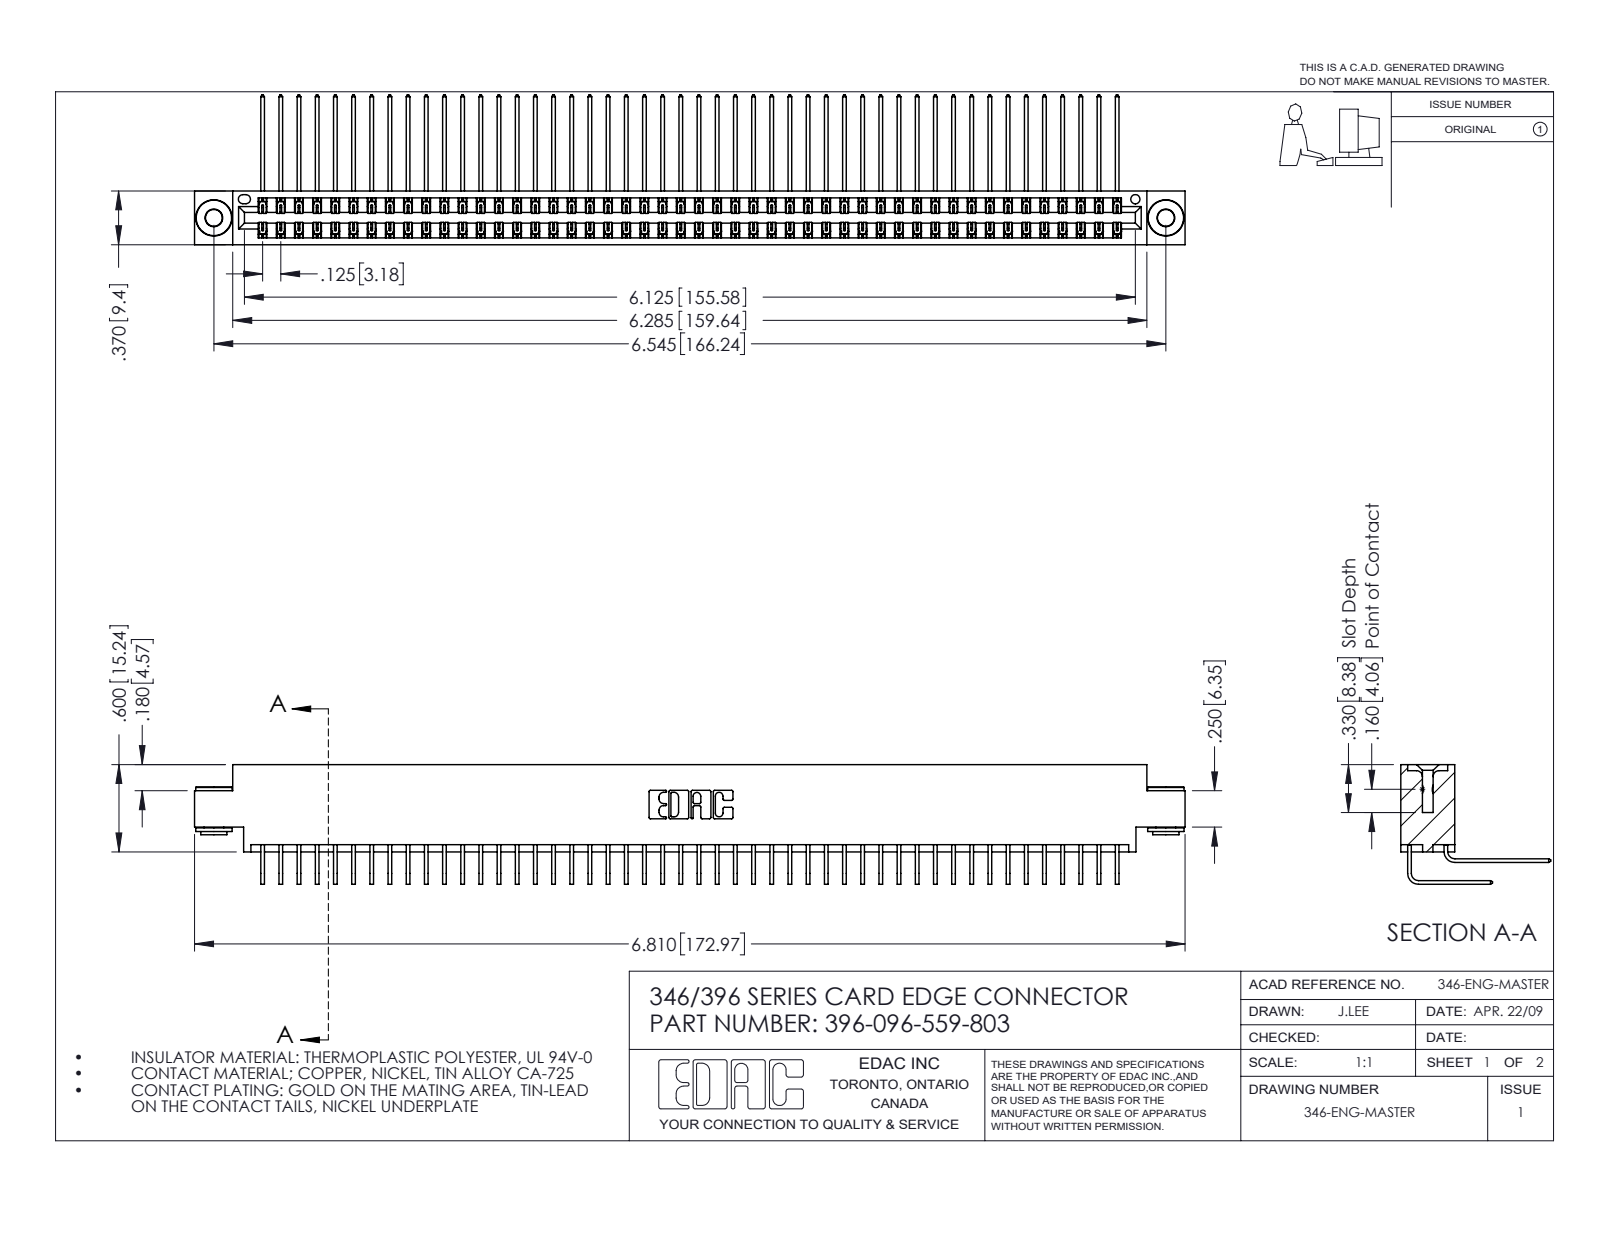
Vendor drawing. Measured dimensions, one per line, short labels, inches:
name: 396-096-559-803; 345-250-002_345-250-002-102; 346 Part_0.170 Offset - 0.156 Dia-TH; 345-292-001_558 559 Tail - 1 (+1 more)
written by: SolidWorks 2016 (CONFIG_CONTROL_DESIGN)
unit: in
bodies: 99 solids, 5348 faces (3642 planar, 1698 cylindrical, 8 other)
size: 6.81 × 1.03 × 0.823
volume: 1.058 in³; area: 41.8 in²
holes: 2× ⌀0.116, 2× ⌀0.156, 1× ⌀0.064
bosses: 2× ⌀0.25, 2× ⌀0.18, 2× ⌀0.136
rounds: 144× R0.006, 22× R0.01, 6× R0.007, 6× R0.031, 3× R0.026, 2× R0.014, 2× R0.022, 2× R0.024
face distances: 0.048, 0.322, 0.025, 0.37, 0.25, 0.072, 0.298, 0.275, 0.148, 0.222
hole spacings: 0.246, 6.336, 6.545
